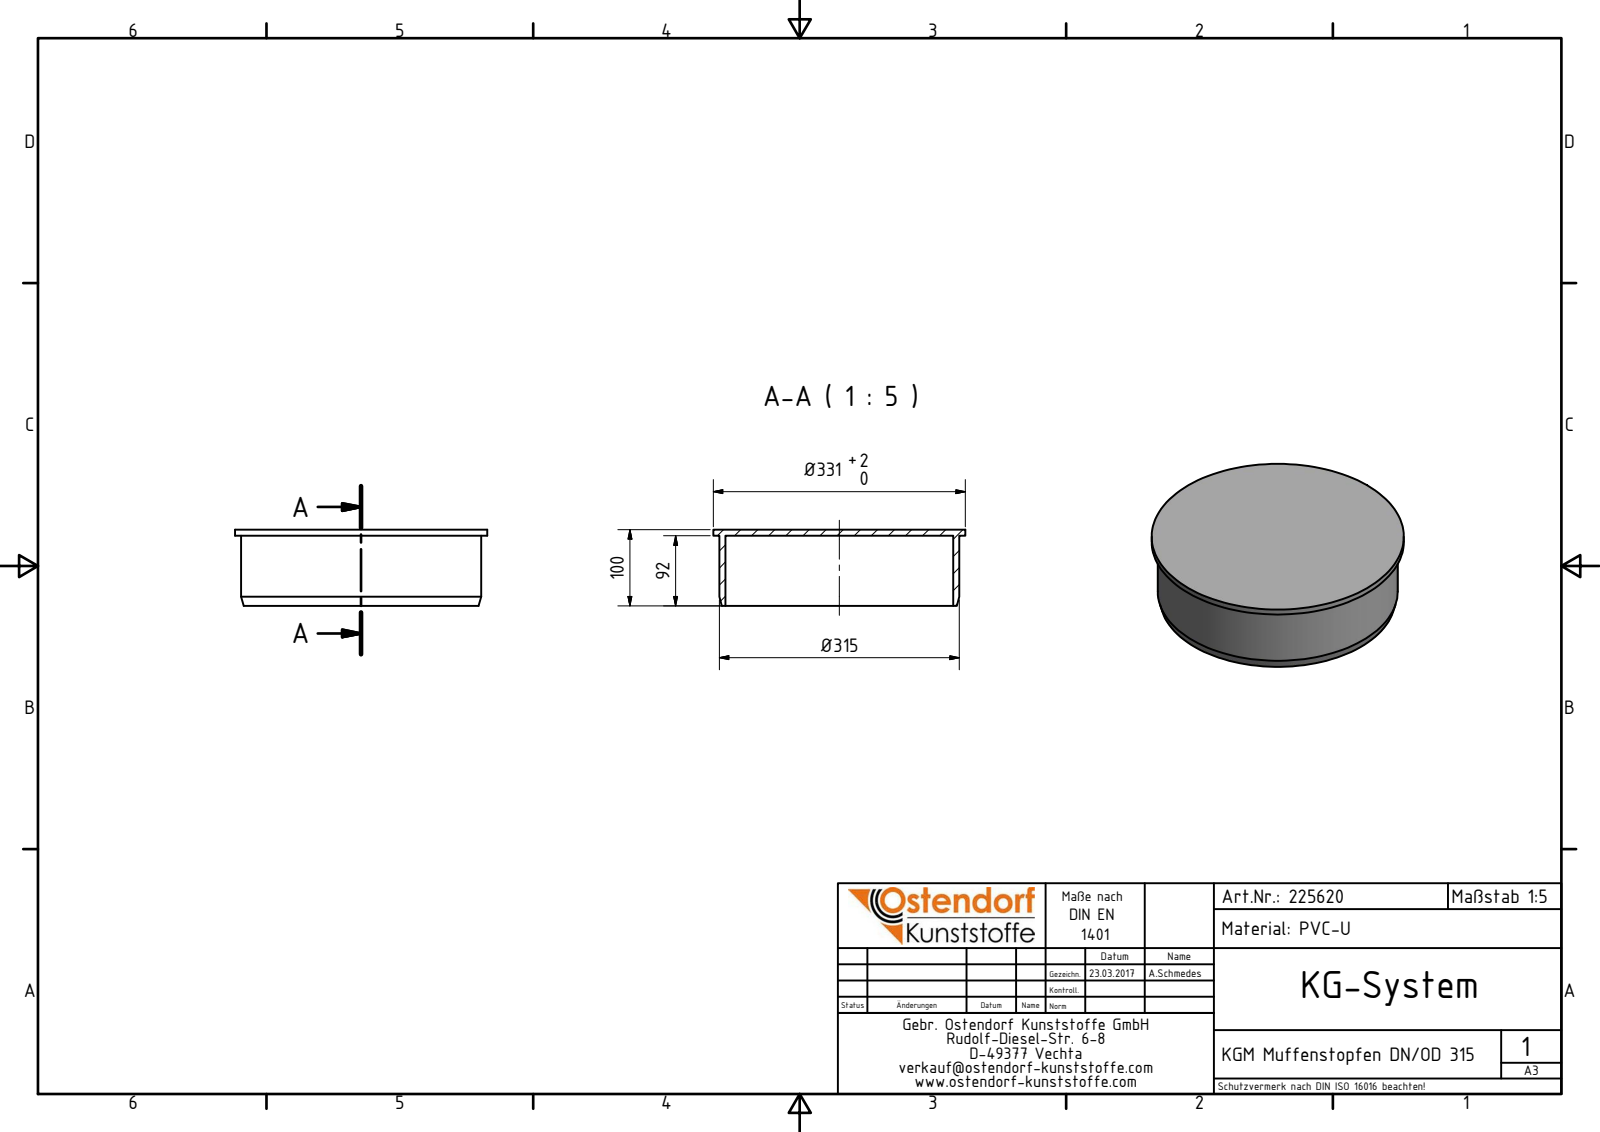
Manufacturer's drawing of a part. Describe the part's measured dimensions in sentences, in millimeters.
The part is named "225620 KGM Muffenstopfen DN_OD 315". Its 3-D file was written by "Autodesk Inventor 2016 (AUTOMOTIVE_DESIGN)". It is 1 solid with 8 faces: 4 planar, 3 cylindrical and 1 other. Overall it measures 331 by 331 by 100 millimeters. Its volume is 1 379 000 cubic millimeters and its surface area 355 023 square millimeters. Round holes: 1 of diameter 299. Round bosses or shafts: 1 of diameter 331, 1 of diameter 315. The main face-to-face distances are 8, 92, 100.
